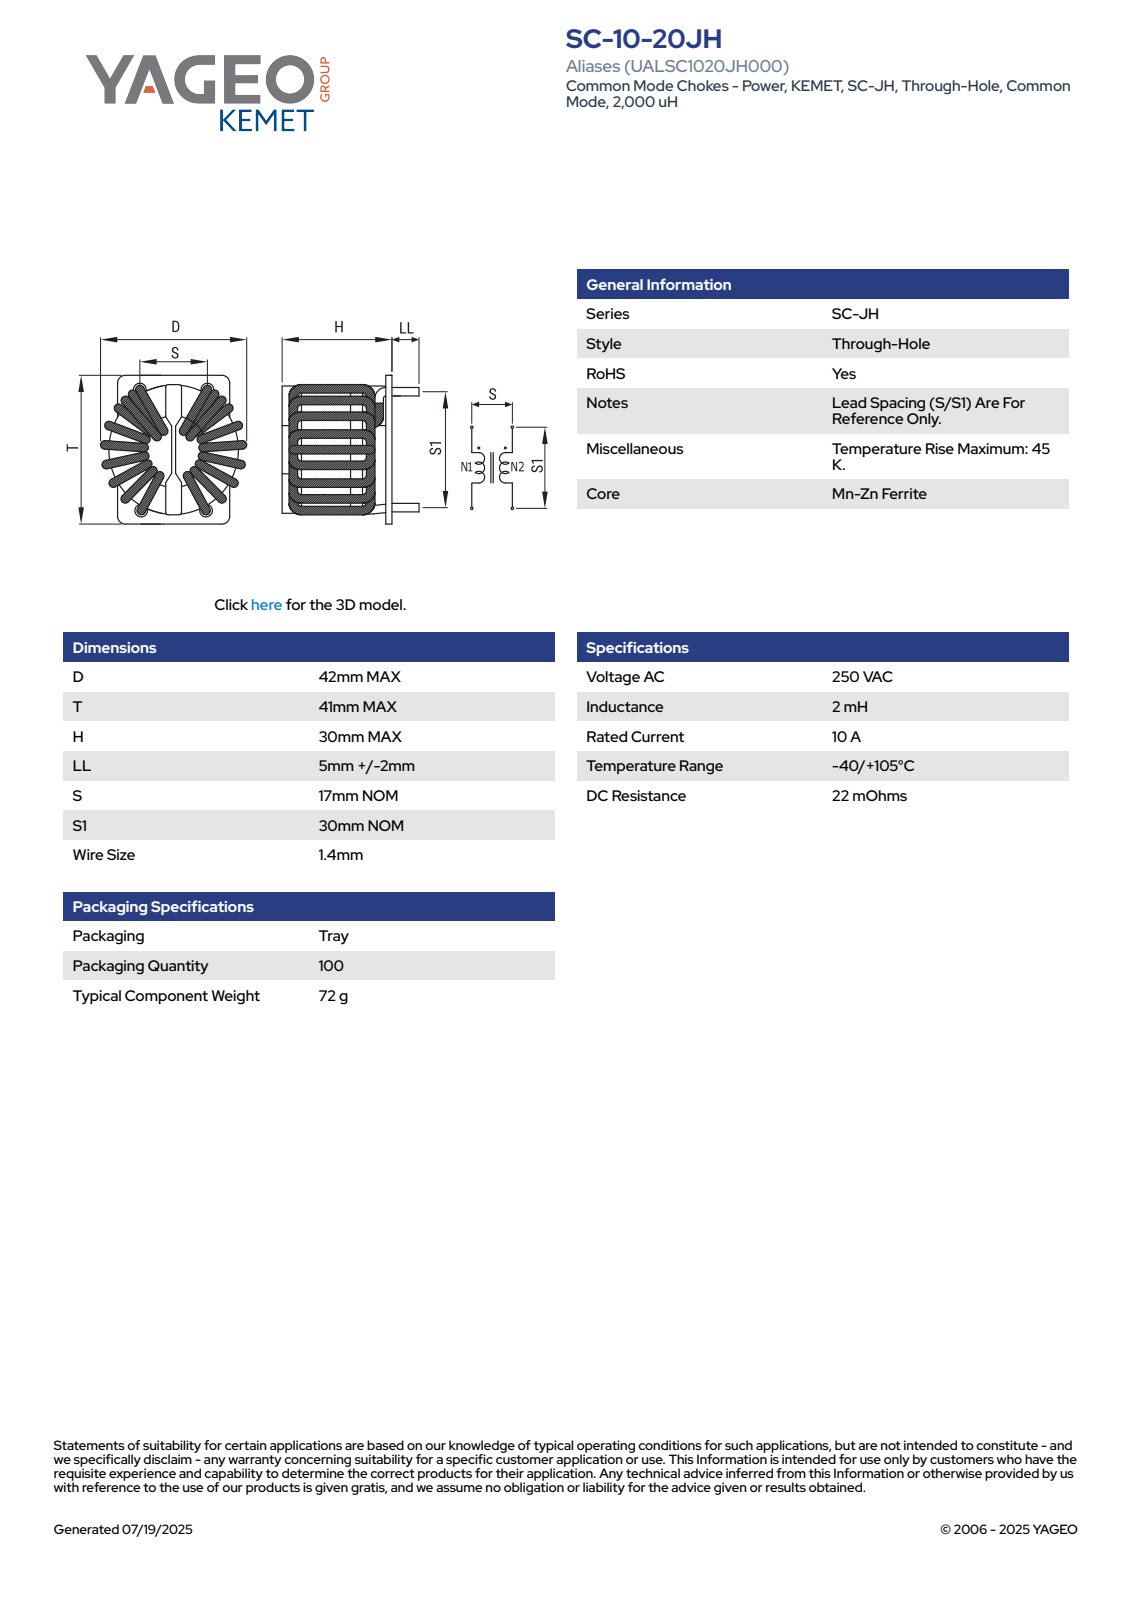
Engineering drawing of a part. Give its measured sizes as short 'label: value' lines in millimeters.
name: SC-10-20JH
written by: SolidWorks 2018 (AUTOMOTIVE_DESIGN)
unit: mm
bodies: 1 solid, 495 faces (235 planar, 150 cylindrical, 110 other)
size: 42 × 41 × 35
volume: 27 556 mm³; area: 13 459 mm²
holes: 4× ⌀1.8
bosses: 10× ⌀1.4
rounds: 30× R0.7, 22× R0.5, 8× R0.8, 4× R6, 2× R1, 1× R0.4, 1× R6.6, 1× R8.8
face distances: 2.8, 28.4, 5.6, 25.6, 22.8, 0.8, 1.35, 2.15, 1, 3.9
hole spacings: 17, 30, 34.48
